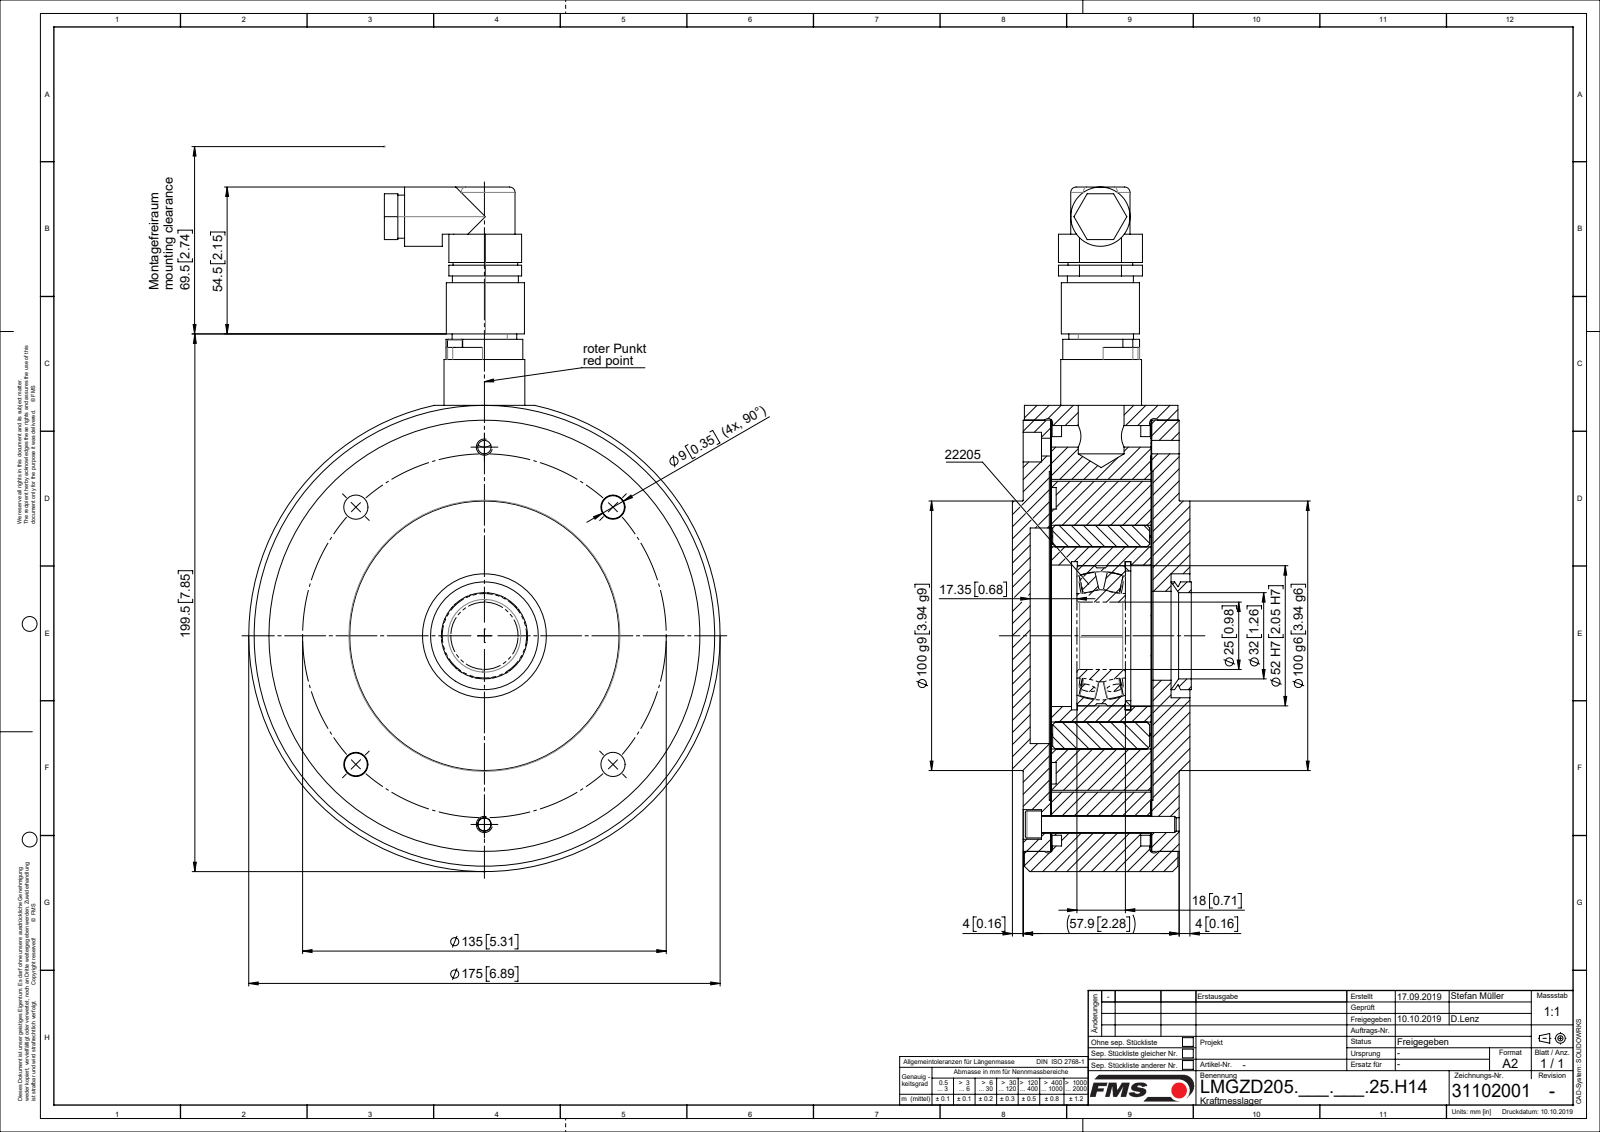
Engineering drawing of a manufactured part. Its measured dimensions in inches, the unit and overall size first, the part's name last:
Units: inches
Overall size (bounding box): 10 × 6.89 × 2.614
Round holes (diameter × count): ⌀0.098 ×6, ⌀0.354 ×4, ⌀0.126 ×3, ⌀0.134 ×2, ⌀0.142 ×2, ⌀0.197 ×2, ⌀0.26 ×2, ⌀0.315 ×2, ⌀0.335 ×2, ⌀0.433 ×2, ⌀0.394 ×1, ⌀0.551 ×1
Round bosses / shafts (diameter × count): ⌀0.085 ×13, ⌀0.945 ×2, ⌀0.866 ×2, ⌀0.217 ×2, ⌀0.118 ×2, ⌀6.89 ×1, ⌀6.299 ×1, ⌀5.827 ×1
Partial cylindrical surfaces — rounded edges, fillets, slot ends (radius × count): R0.004 ×4, R0.079 ×2, R0.118 ×2, R0.167 ×2, R0.295 ×2, R0.354 ×2, R0.433 ×2, R0.819 ×1
Main face-to-face distances: 1.467, 0.402, 0.411, 1.868, 1.878, 1.457, 1.476, 0.02, 0.382, 1.898
Hole centre spacings: 0.64, 0.885, 0.906, 1.926, 2.074, 2.657, 3.758, 3.829
Volume: 82.02 in³ · Surface area: 440.8 in²
Bodies: 48 solids, 783 faces (215 planar, 303 cylindrical, 265 other)
Part name (STEP PRODUCT): 31101677_V-032A; 47664_01; Zyl-Schr DIN912_M3x25; 49027_01 (+8 more)
STEP written by: SolidWorks 2018 (CONFIG_CONTROL_DESIGN)
